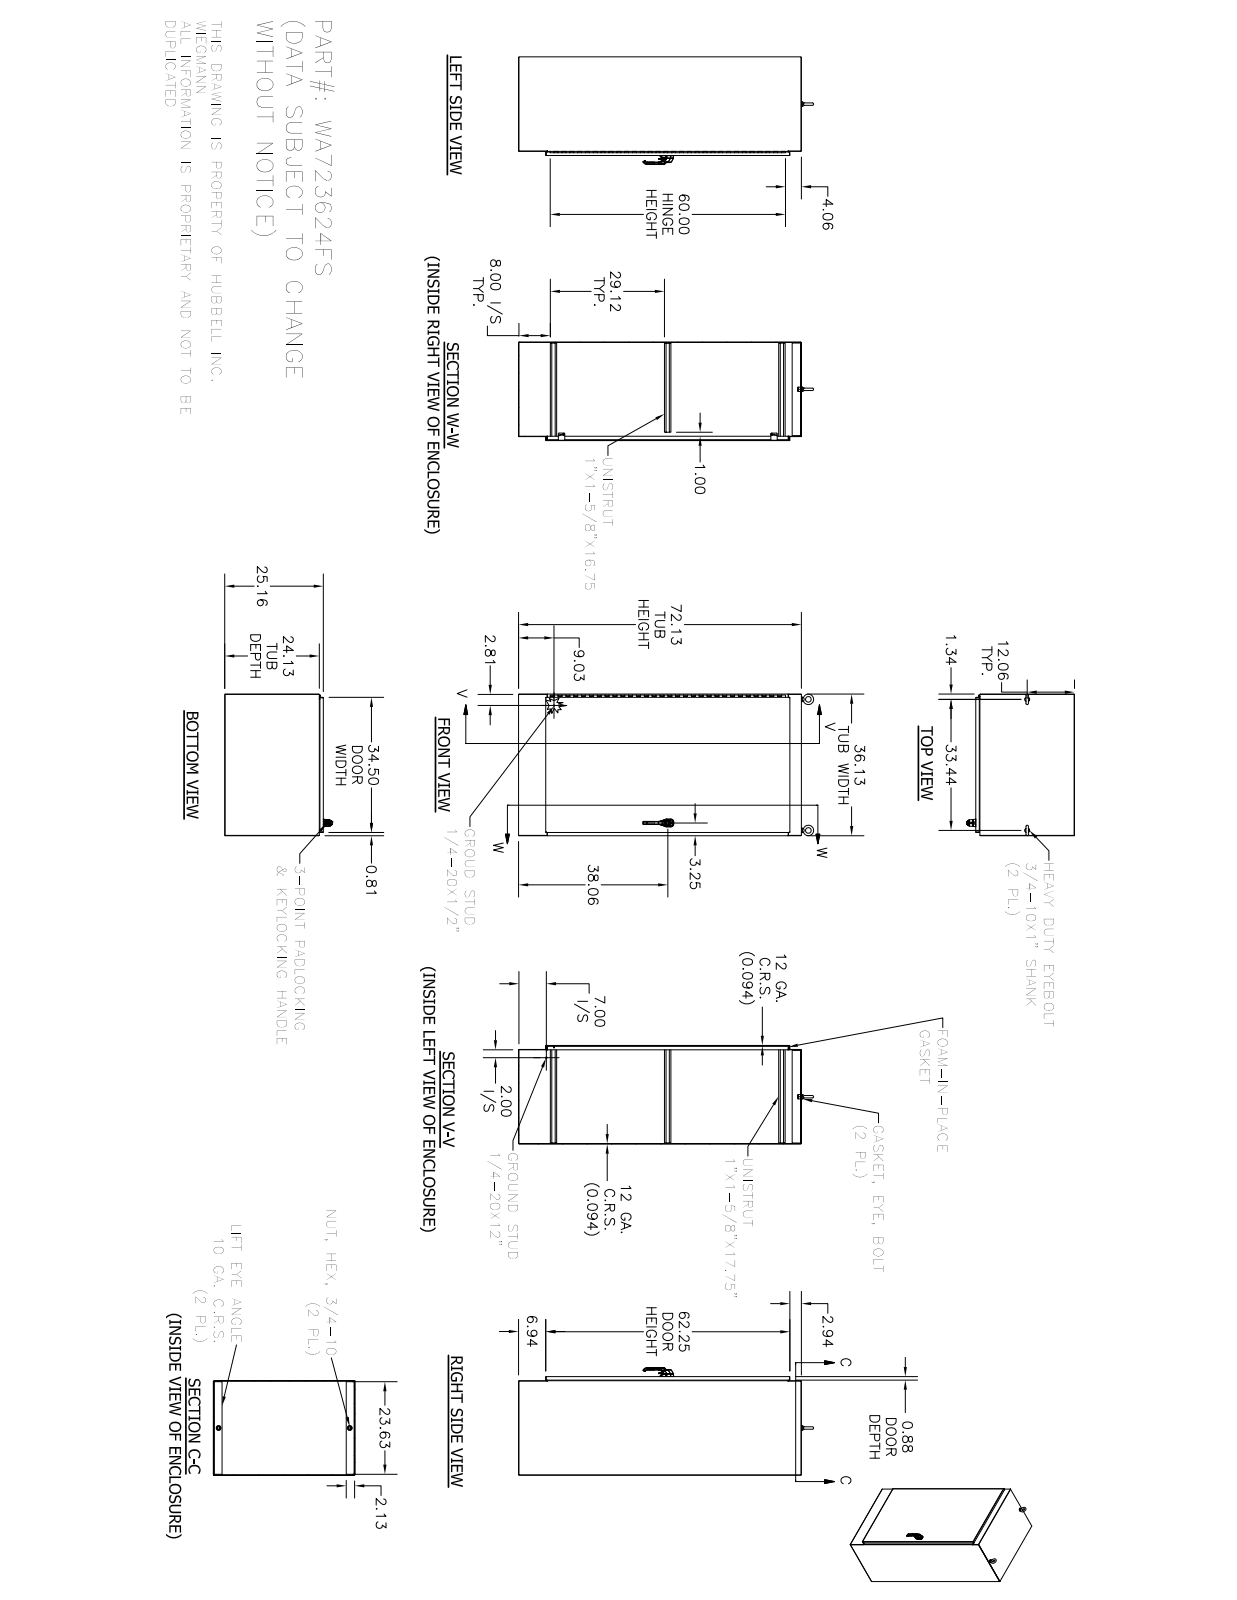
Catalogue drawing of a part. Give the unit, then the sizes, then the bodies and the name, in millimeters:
Units: millimetres
Overall size (bounding box): 1911.29 × 917.58 × 696.2
Round holes (diameter × count): ⌀7.02 ×8, ⌀5.08 ×4, ⌀5.4 ×3, ⌀7.11 ×3, ⌀8 ×2, ⌀10.2 ×2, ⌀10.33 ×2, ⌀10.5 ×2, ⌀16.31 ×2, ⌀20.64 ×2, ⌀3.1 ×1, ⌀3.15 ×1
Round bosses / shafts (diameter × count): ⌀6.35 ×3, ⌀31.75 ×2, ⌀28.45 ×2, ⌀19.05 ×2, ⌀13.5 ×2, ⌀13.37 ×2, ⌀11.05 ×2, ⌀8.56 ×2
Partial cylindrical surfaces — rounded edges, fillets, slot ends (radius × count): R0.5 ×170, R0.3 ×100, R0.47 ×21, R0.25 ×16, R0.79 ×15, R2 ×14, R3.17 ×13, R0.48 ×12
Main face-to-face distances: 2.38, 636.7, 915.2, 634.32, 639.08, 912.82, 1829.6, 917.58, 610.4, 26.3
Hole centre spacings: 9.66, 9.7, 9.71, 19.36, 19.4, 22.5, 29.06, 32.29
Volume: 18 280 000 mm³ · Surface area: 15 250 000 mm²
Bodies: 46 solids, 2855 faces (1212 planar, 995 cylindrical, 648 other)
Part name (STEP PRODUCT): WA723624FSBLS; WA7224FSRS; WA3624FSTOP; WA3624FSBTM (+8 more)
STEP written by: Autodesk Inventor 2014 (AUTOMOTIVE_DESIGN)
